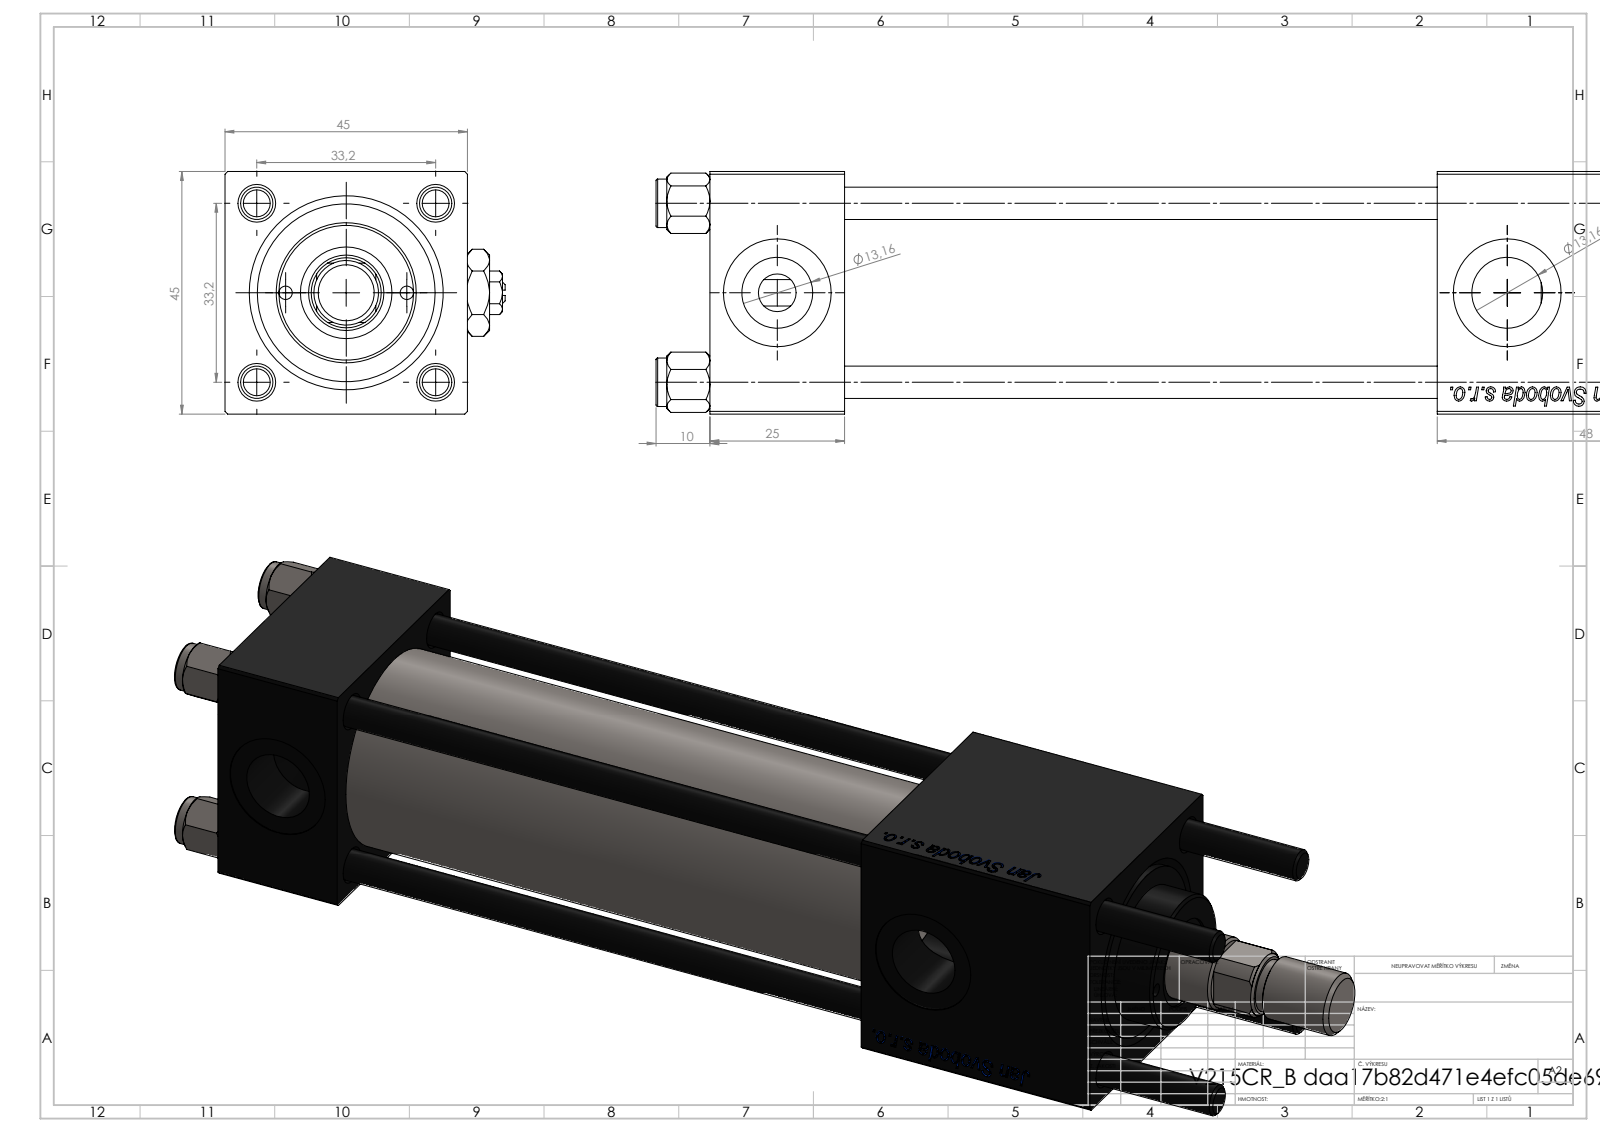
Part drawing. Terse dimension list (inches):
name: V215CR_VCP_B; V215_VC_A; V215CR_B-1; ROD_END_AH (+3 more)
written by: SolidWorks 2019 (CONFIG_CONTROL_DESIGN)
unit: in
bodies: 13 solids, 1228 faces (460 planar, 92 cylindrical, 676 other)
size: 9.213 × 2.047 × 1.772
volume: 14.34 in³; area: 147.3 in²
holes: 4× ⌀0.236, 2× ⌀0.098, 2× ⌀0.276, 2× ⌀0.518, 2× ⌀0.787, 1× ⌀0.256, 1× ⌀0.551, 1× ⌀0.669, 1× ⌀0.945, 1× ⌀1.26, 1× ⌀1.299
bosses: 4× ⌀0.354, 1× ⌀1.496, 1× ⌀1.024, 1× ⌀0.472, 1× ⌀0.394
rounds: 1× R0.256
face distances: 1.772, 0.984, 7.205, 6.22, 5.315, 4.331, 1.89, 6.075, 5.091, 0.76
hole spacings: 0.687, 0.924, 1.276, 1.307, 0.443, 1.848, 0.886, 5.335
